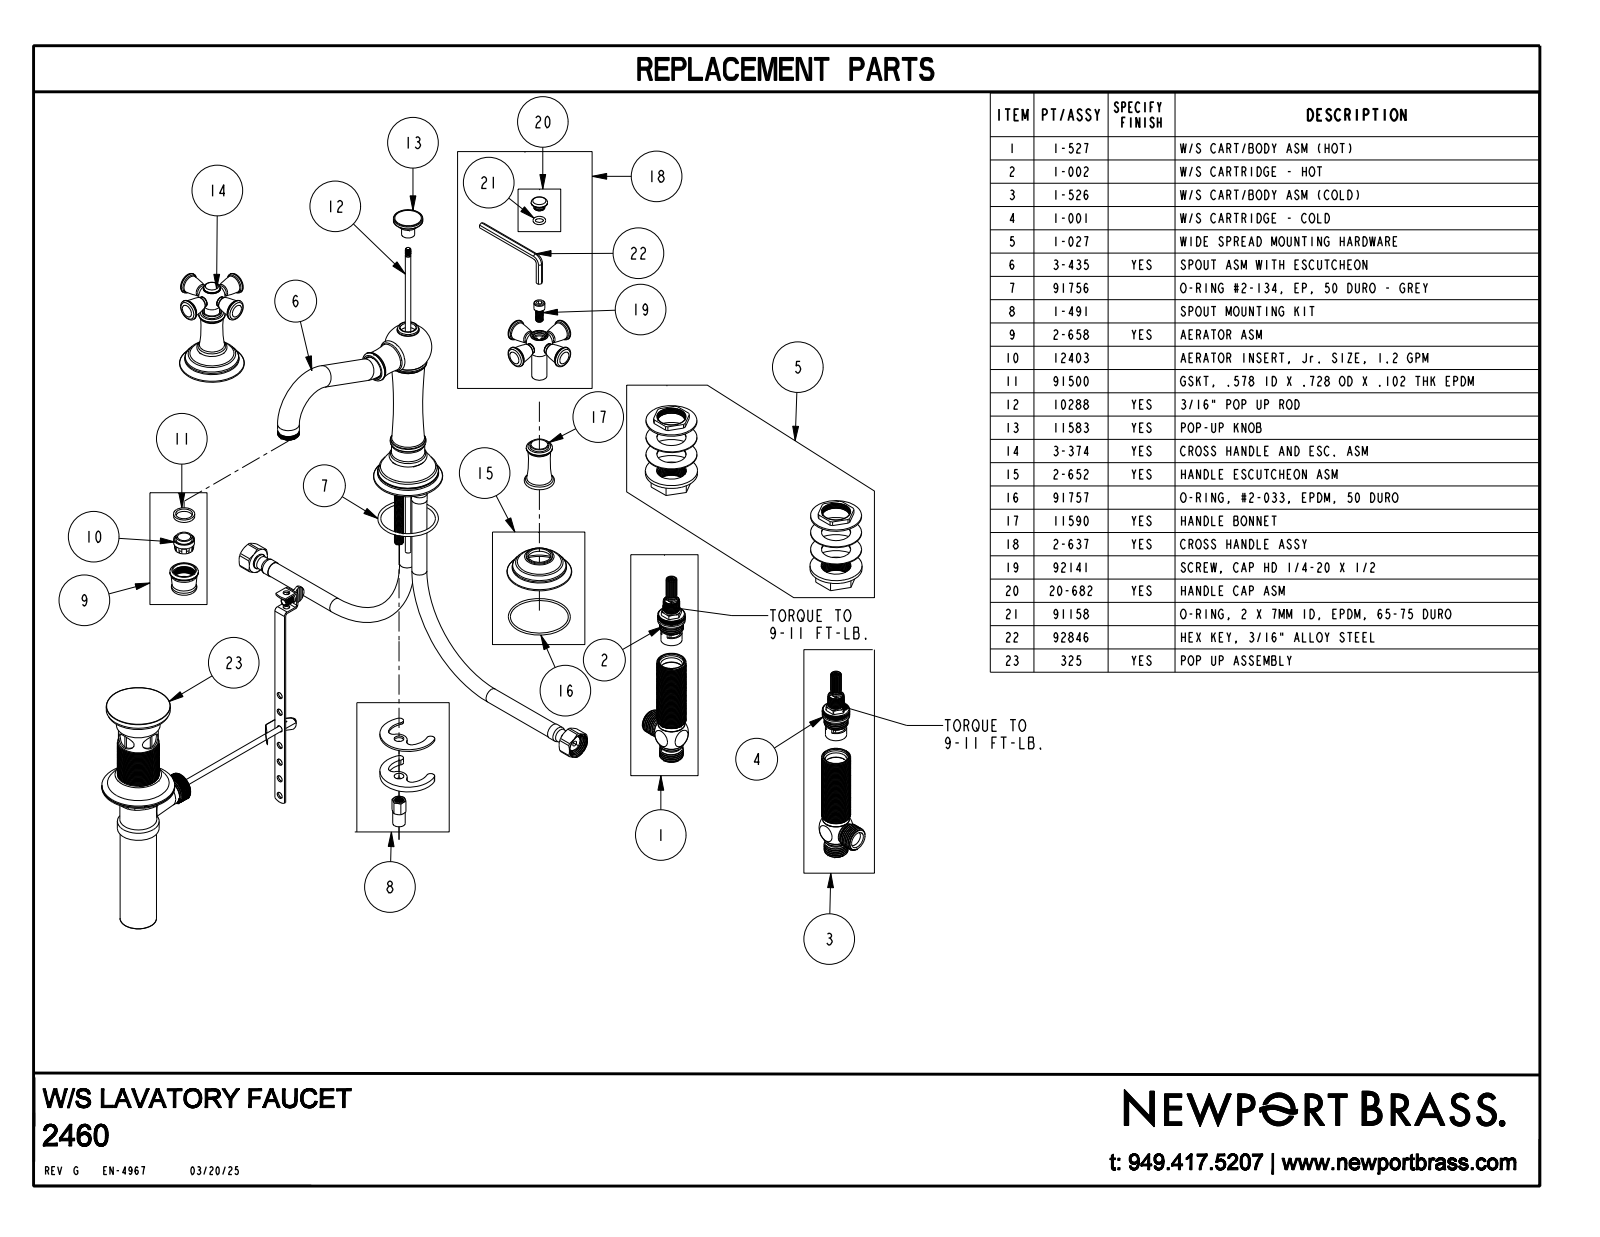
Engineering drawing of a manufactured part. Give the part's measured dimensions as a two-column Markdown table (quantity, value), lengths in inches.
| quantity | value |
| --- | --- |
| part name | 2460 |
| STEP written by | CREO PARAMETRIC BY PTC INC, 2018400 (CONFIG_CONTROL_DESIGN) |
| units | inches |
| bodies | 3 solids, 379 faces (23 planar, 70 cylindrical, 286 other) |
| overall size | 10.528 × 7.806 × 6.892 |
| volume | 19.37 in³ |
| surface area | 99.04 in² |
| round holes (diameter × count) | 0.543 × 1 |
| round bosses / shafts (diameter × count) | 0.75 × 3, 0.72 × 3, 0.36 × 3, 0.9 × 2, 0.649 × 2, 0.56 × 2, 0.517 × 2, 1.281 × 1 |
| main face-to-face distances | 4.201, 2.14, 2.061, 2.22, 0.08, 1.981, 1.05, 4.971, 2.831, 2.751 |
